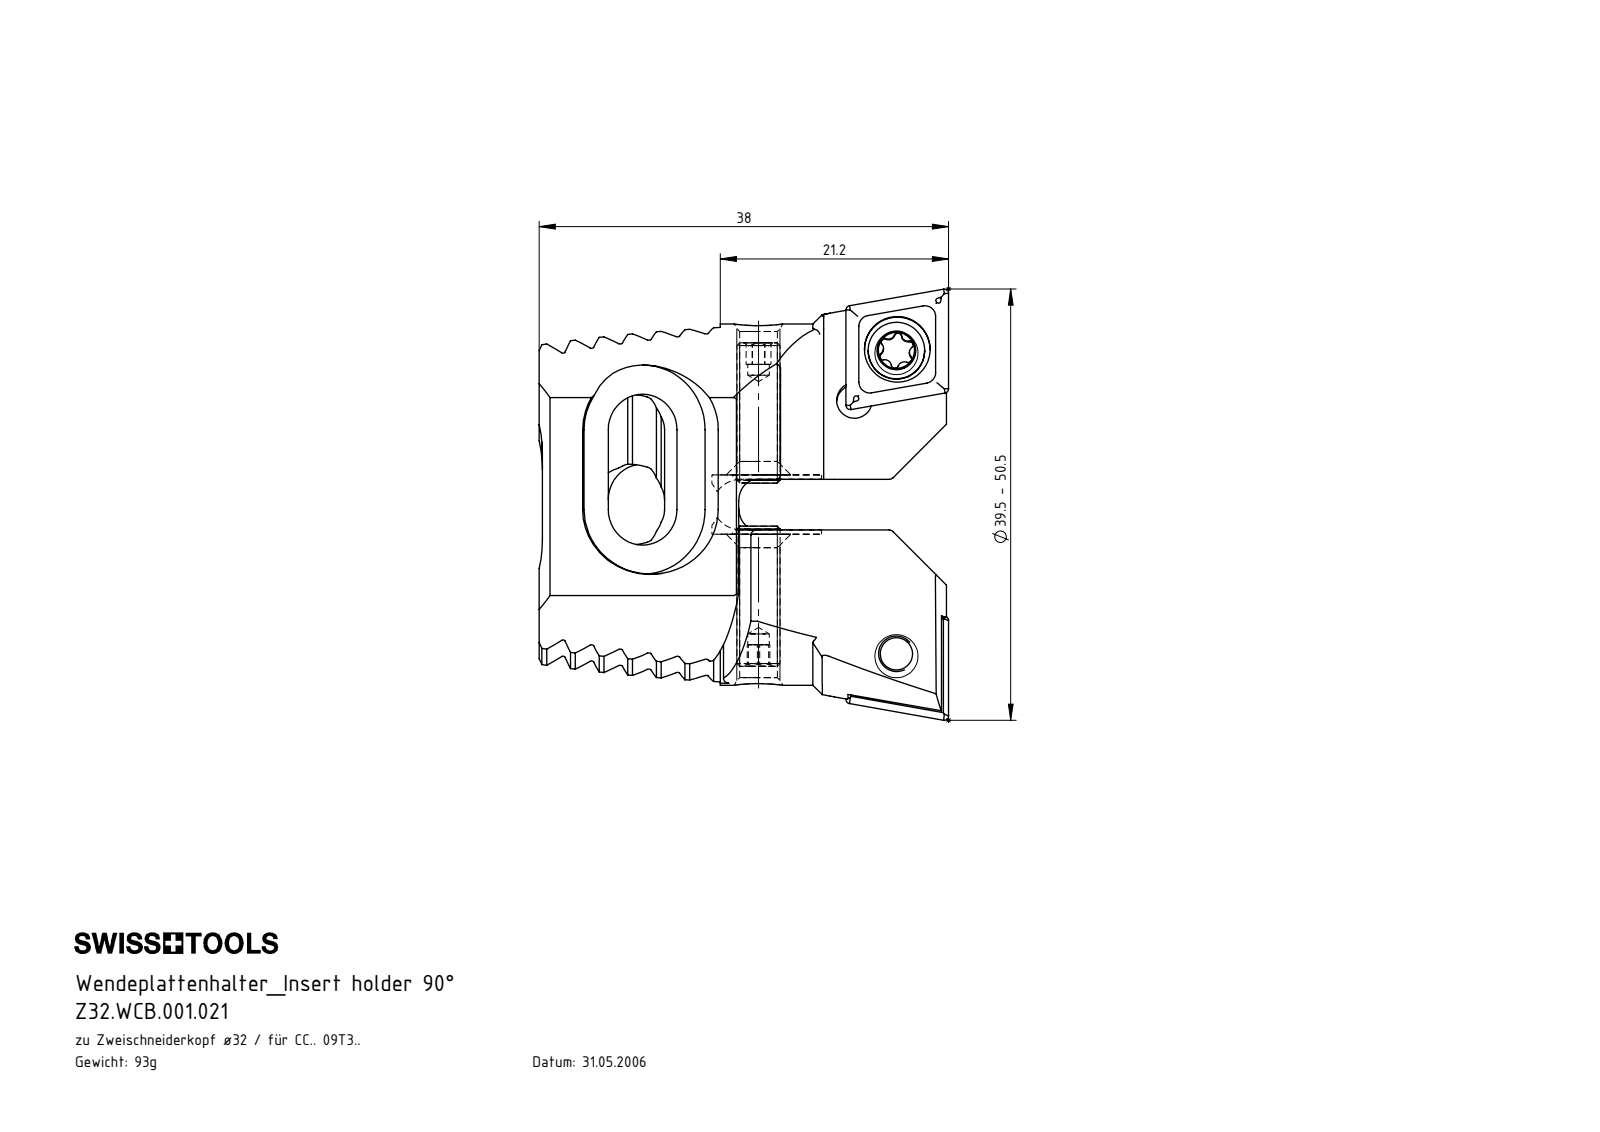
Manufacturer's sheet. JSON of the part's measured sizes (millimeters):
{"part_name": "Z32-WCB.001.021; Z32-ER3.001.013_A; CCMT09T304; WCB-ER2.001.009_A (+1 more)", "step_written_by": "SolidWorks 2012 (CONFIG_CONTROL_DESIGN)", "units": "millimeters", "bodies": {"solids": 8, "faces": 626, "planar": 282, "cylindrical": 132, "other": 212}, "overall_size": [40, 38, 26.2], "volume_mm3": 11881, "surface_area_mm2": 8255, "round_holes": [[3.3, 4], [1.6, 2], [4.4, 2], [6.1, 2], [3.5, 1]], "round_bosses_or_shafts": [[4, 3], [5.25, 2]], "partial_cylinders_radius": [[0.5, 16], [0.2, 12], [0.34, 12], [0.59, 12], [2, 4], [3.3, 4], [6, 4], [12, 4]], "face_to_face_distances": [2.38, 4.76, 9.53, 7.15, 4.89, 11.91, 7.14, 1.27, 4.77, 2.39], "hole_center_spacings": [6.07, 6.19, 9, 24.23, 24.33, 28.65, 17.38, 19.27]}
